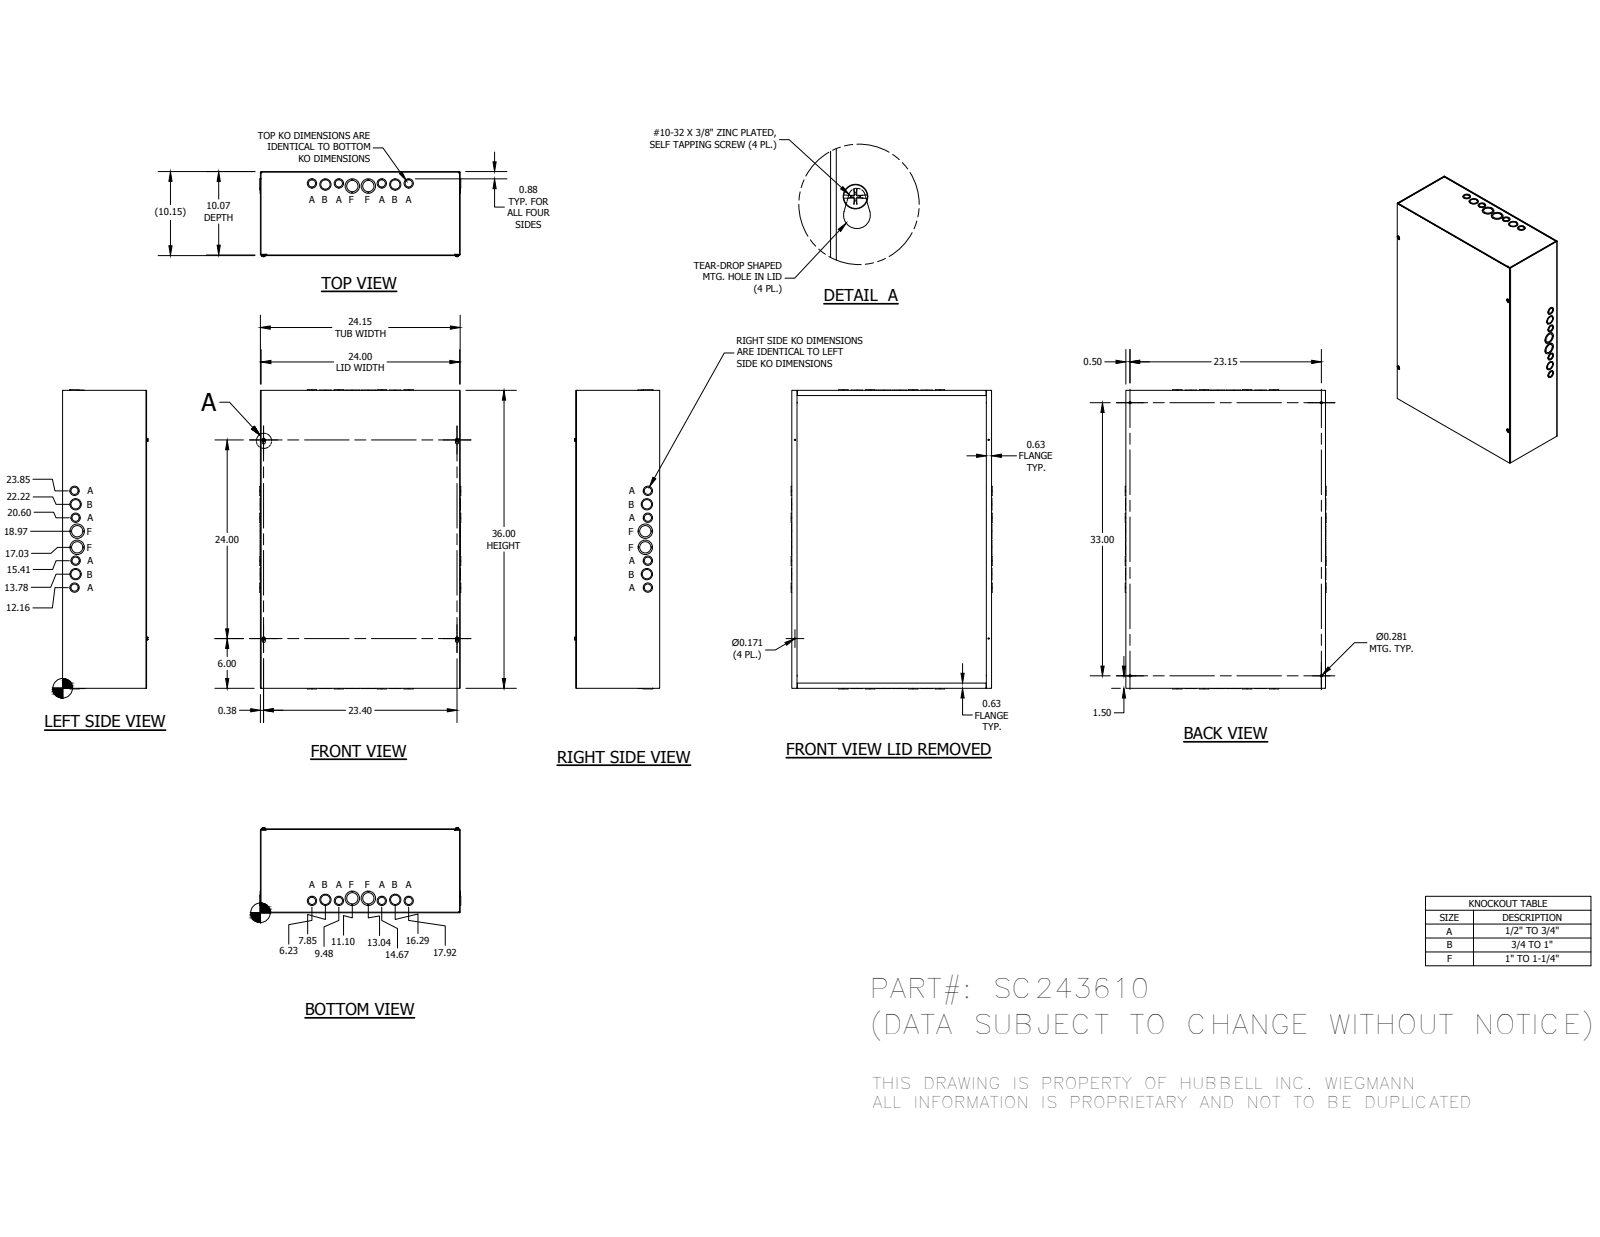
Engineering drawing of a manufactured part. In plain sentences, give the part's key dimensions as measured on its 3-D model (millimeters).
The part is named "SC243610BLR; SC2410TB; SC2436LPA; 37214 (+1 more)". Its 3-D file was written by "Autodesk Inventor 2014 (AUTOMOTIVE_DESIGN)". It is 37 solids with 1219 faces: 899 planar, 236 cylindrical and 84 other. Overall it measures 918.16 by 617.12 by 261.11 millimeters. Round holes: 14 of diameter 28.57, 10 of diameter 22.22, 8 of diameter 34.92, 4 of diameter 4.34, 4 of diameter 7.14, 4 of diameter 44.45. Round bosses or shafts: 4 of diameter 4.83. Partial cylindrical surfaces (rounded edges, fillets, slot ends): 12 of radius 0.4, 12 of radius 2.28, 4 of radius 3.17, 4 of radius 5.16. The main face-to-face distances are 1.88, 255.88, 254, 257.76, 611.48, 912.52, 609.6, 613.36, 914.4, 910.64. The hole center spacings are 41.39, 41.4, 42.03, 82.55, 82.69, 90.9, 114.34, 124.07.
